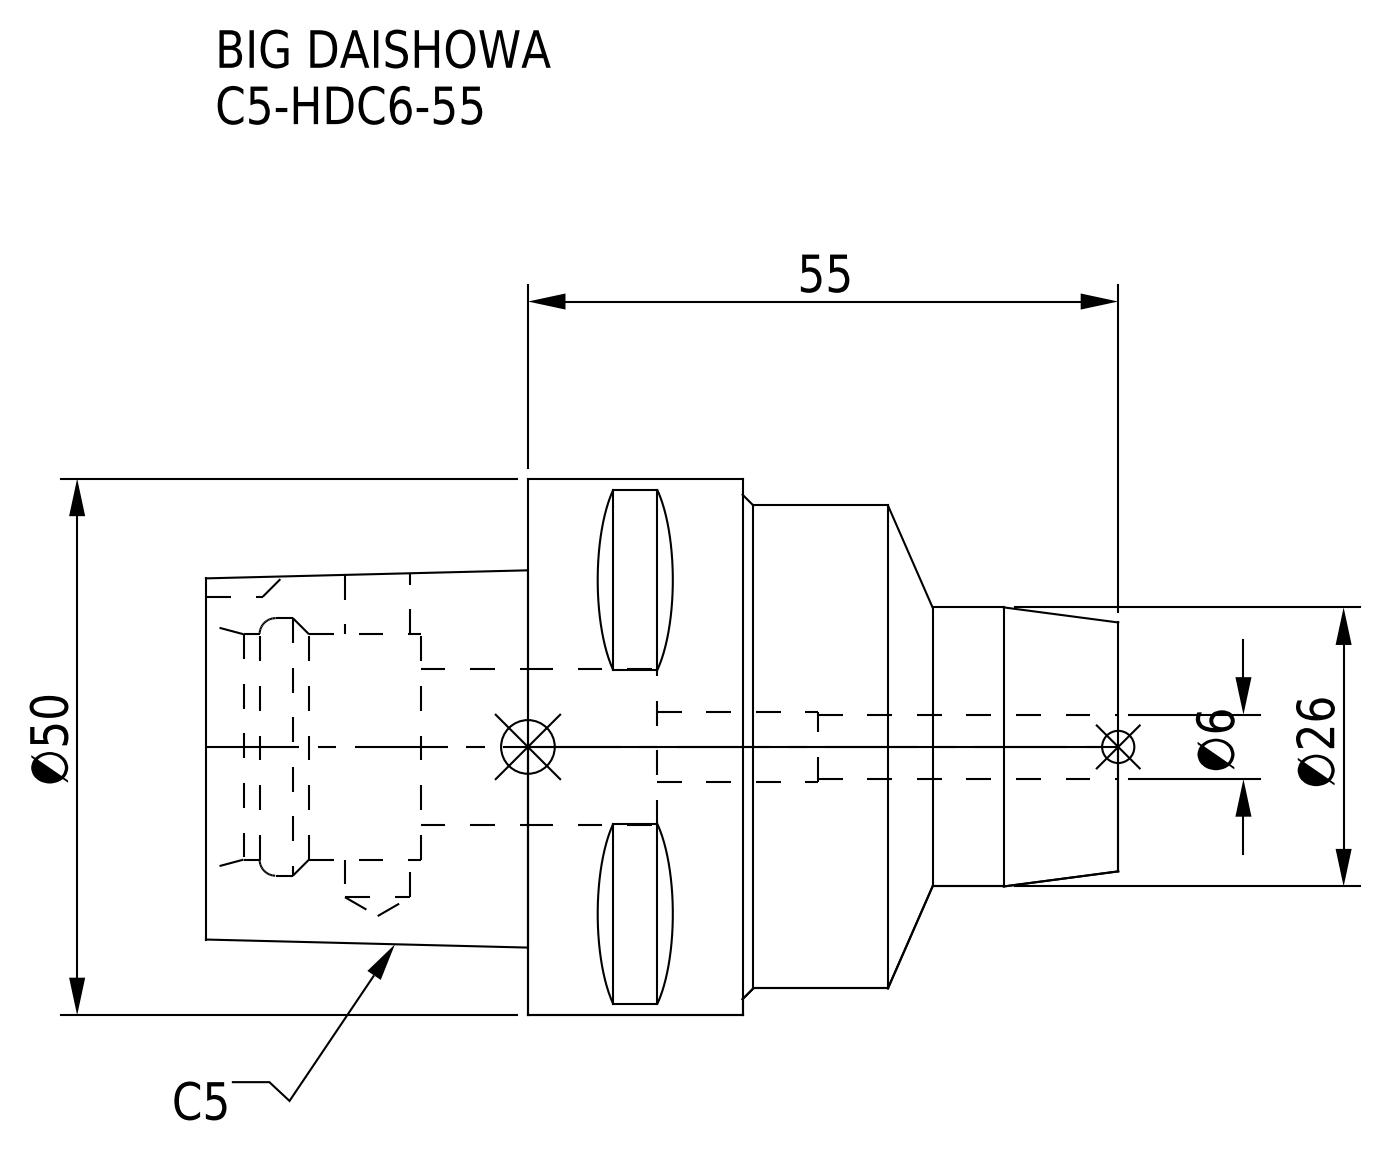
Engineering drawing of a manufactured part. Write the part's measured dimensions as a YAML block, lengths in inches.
part_name: "C5-HDC6-55"
step_written_by: "CREO PARAMETRIC BY PTC INC, 2016380 (AUTOMOTIVE_DESIGN)"
units: inches
bodies: {solids: 1, faces: 68, planar: 29, cylindrical: 23, other: 16}
overall_size: [3.346, 1.969, 1.969]
volume: 5.347
surface_area: 26.27
round_holes:
  - {diameter: 0.236, count: 1}
  - {diameter: 0.24, count: 1}
  - {diameter: 0.256, count: 1}
  - {diameter: 0.571, count: 1}
  - {diameter: 0.827, count: 1}
  - {diameter: 0.945, count: 1}
round_bosses_or_shafts:
  - {diameter: 1.969, count: 1}
  - {diameter: 1.772, count: 1}
  - {diameter: 1.024, count: 1}
partial_cylinders:
  - {radius: 0.157, count: 1}
face_to_face_distances: [1.181, 0.787, 2.165, 3.346, 1.378, 1.969, 1.732, 2.559, 0.394, 0.755]
